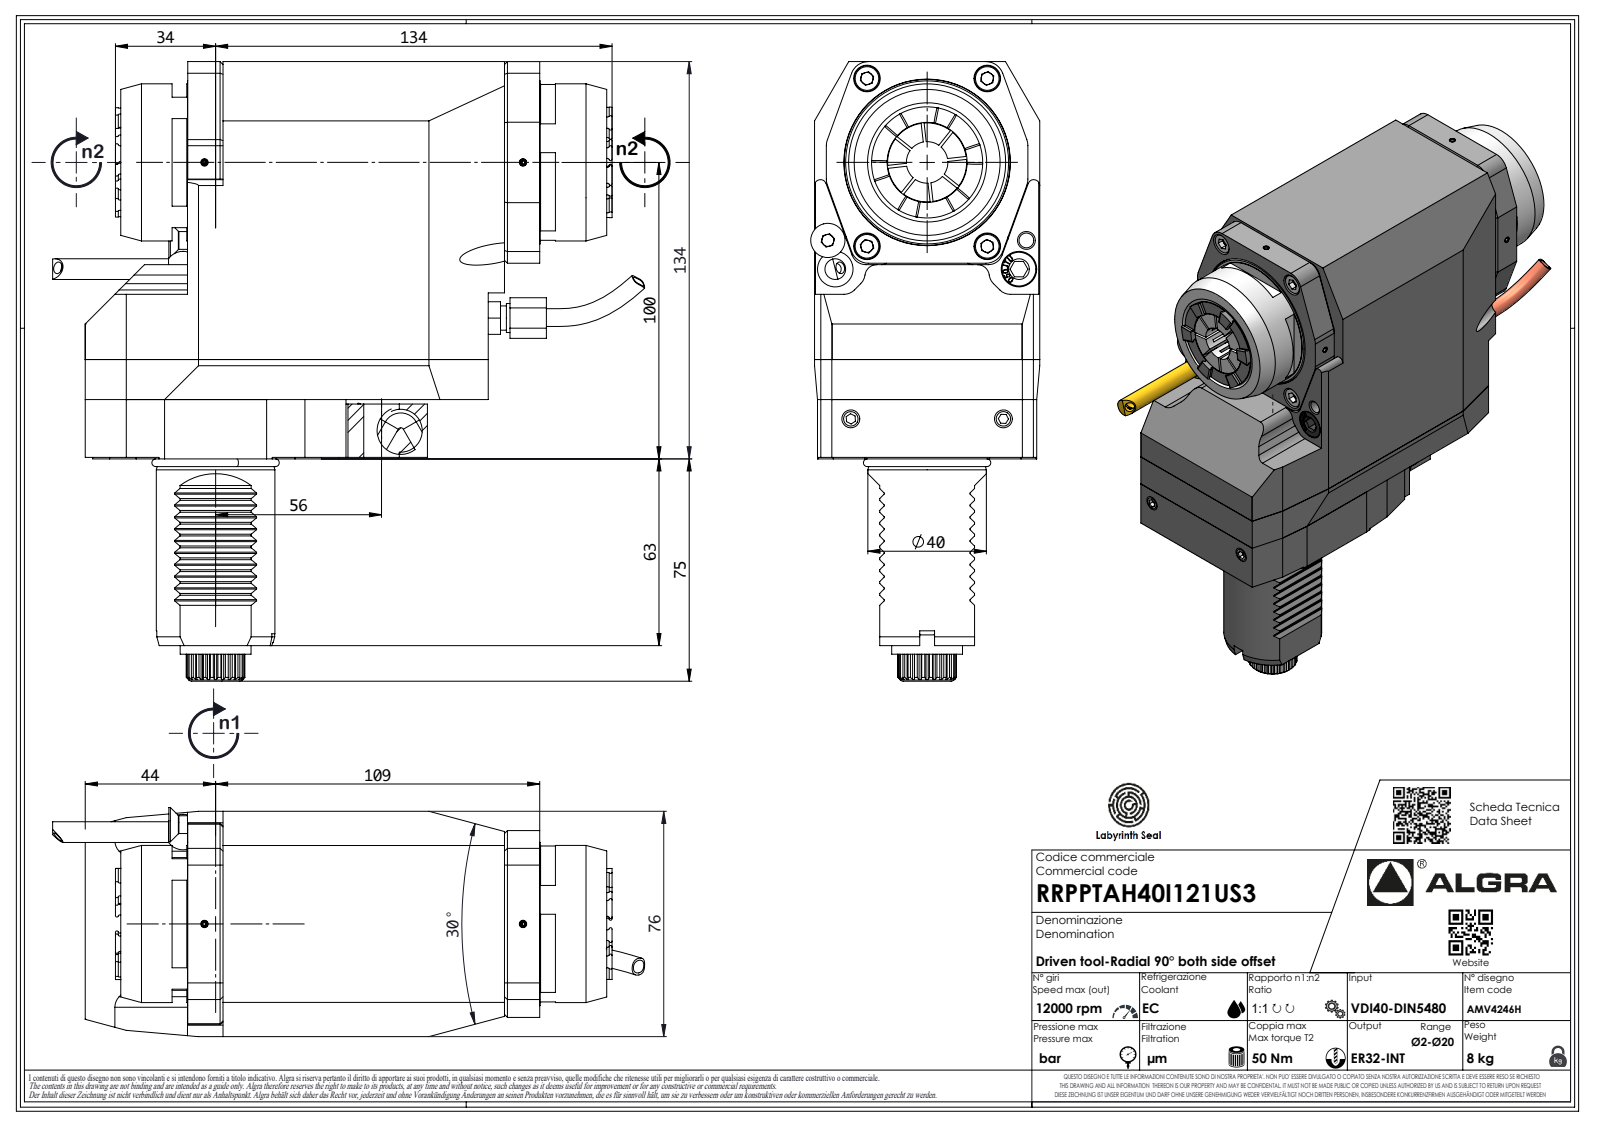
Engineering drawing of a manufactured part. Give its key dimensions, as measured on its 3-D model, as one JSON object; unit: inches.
{"part_name": "RRPPTAH40I121US3", "step_written_by": "SolidWorks 2023 (AUTOMOTIVE_DESIGN)", "units": "inches", "bodies": {"solids": 1, "faces": 728, "planar": 504, "cylindrical": 122, "other": 102}, "overall_size": [8.228, 7.867, 2.992], "volume_in3": 80.92, "surface_area_in2": 145.7, "round_holes": [[0.197, 2], [0.081, 1], [0.083, 1], [0.157, 1]], "round_bosses_or_shafts": [[2.087, 1], [1.575, 1], [1.524, 1], [0.941, 1], [0.386, 1], [0.321, 1], [0.276, 1], [0.251, 1]], "partial_cylinders_radius": [[0.012, 20], [0.236, 10], [0.013, 7], [0.02, 7], [0.146, 7], [0.197, 6], [0.276, 4], [0.079, 3]], "face_to_face_distances": [2.992, 0.472, 0.02, 4.488, 0.787, 5.276, 0.89, 5.567, 0.768, 5.256]}
